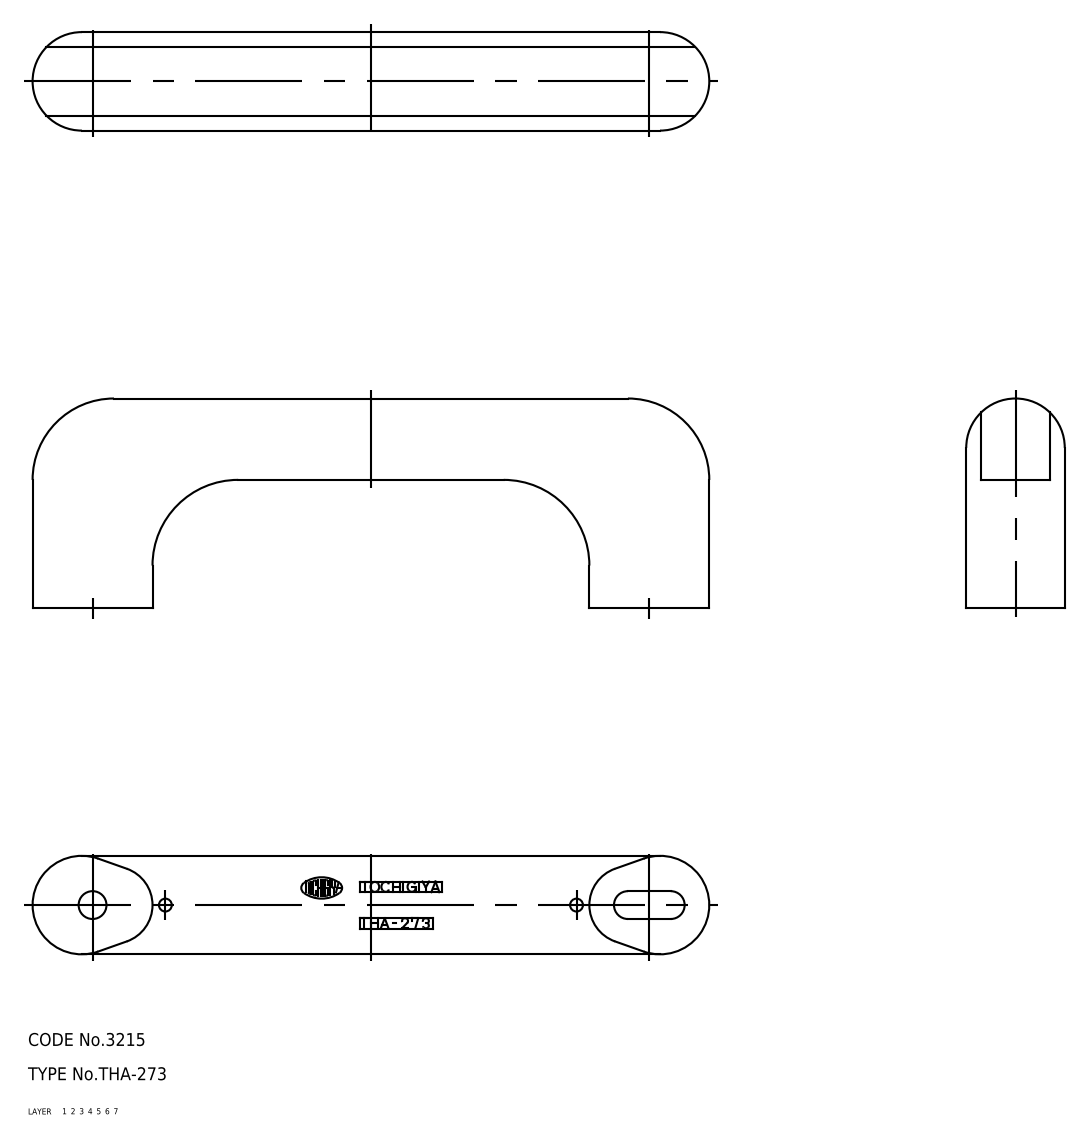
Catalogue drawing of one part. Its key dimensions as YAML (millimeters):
part_name: "pull; cap; THA_273_23692_36"
step_written_by: "CADfix (AUTOMOTIVE_DESIGN)"
units: millimeters
bodies: {solids: 2, faces: 108, planar: 0, cylindrical: 0, other: 108}
overall_size: [158, 49, 23]
volume: 59571
surface_area: 32452
